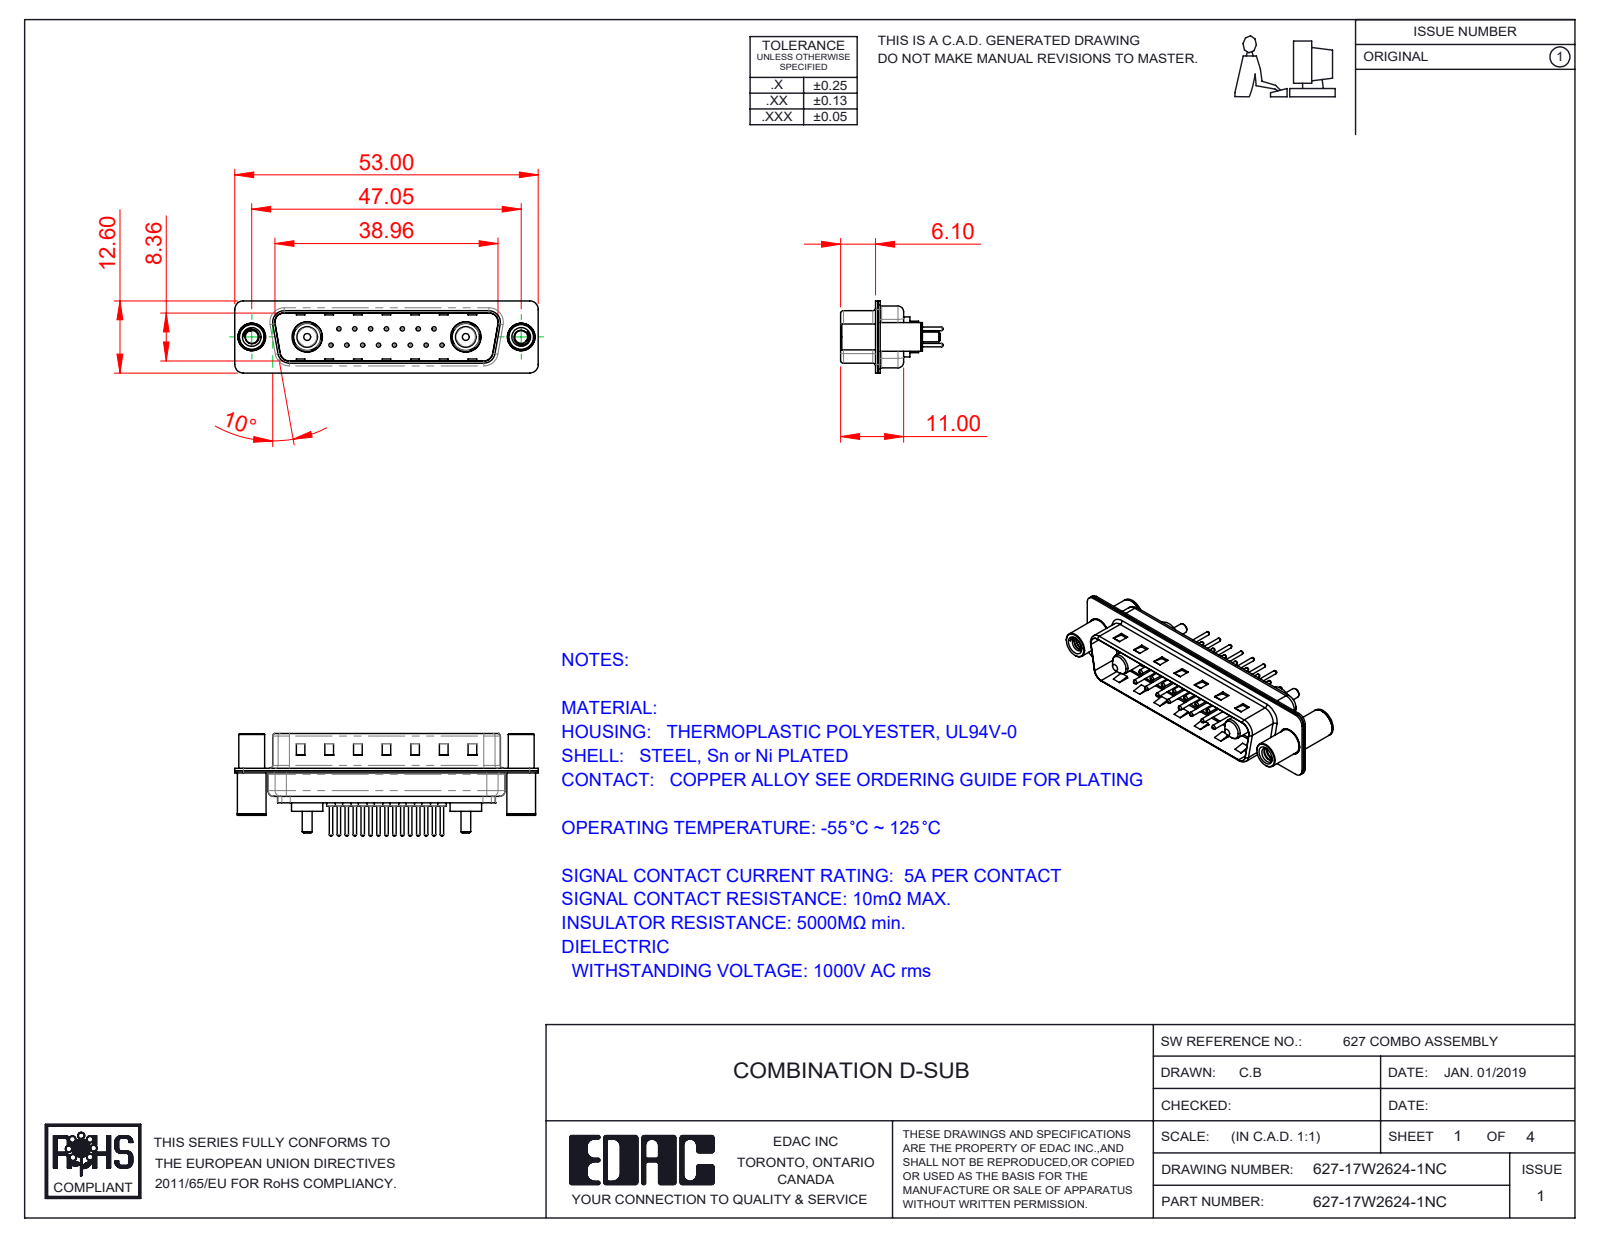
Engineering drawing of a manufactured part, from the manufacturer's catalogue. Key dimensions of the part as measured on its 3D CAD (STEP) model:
Part name (STEP PRODUCT): 627Combo Contact Row 2_24; 627Combo Contact Row 1_24; 627Combo Threaded Standoff and Board Spacer_C; 627-17W2624-1NC (+5 more)
STEP written by: SolidWorks 2016 (CONFIG_CONTROL_DESIGN)
Units: millimetres
Bodies: 24 solids, 1106 faces (302 planar, 447 cylindrical, 357 other)
Overall size (bounding box): 53 × 17.9 × 12.6
Volume: 3 117 mm³ · Surface area: 7 291 mm²
Round holes (diameter × count): ⌀0.75 ×15, ⌀1.6 ×15, ⌀2 ×15, ⌀2.26 ×2, ⌀3.26 ×2, ⌀4 ×2, ⌀4.8 ×2, ⌀4.85 ×2, ⌀5.3 ×2
Round bosses / shafts (diameter × count): ⌀1.5 ×15, ⌀0.6 ×15, ⌀5.5 ×2, ⌀5.2 ×2, ⌀5 ×2, ⌀4.9 ×2, ⌀4.75 ×2, ⌀4.5 ×2
Partial cylindrical surfaces — rounded edges, fillets, slot ends (radius × count): R1.5 ×16, R2 ×12, R0.5 ×8, R1.6 ×8, R0.25 ×4, R0.6 ×4, R0.65 ×4, R0.9 ×4
Main face-to-face distances: 0.4, 0.82, 9.58, 8.76, 1.5, 5.6, 6, 5.2, 0.8, 1.22
Hole centre spacings: 3.16, 2.77, 5.54, 8.31, 5.04, 7.49, 11.08, 5.03
